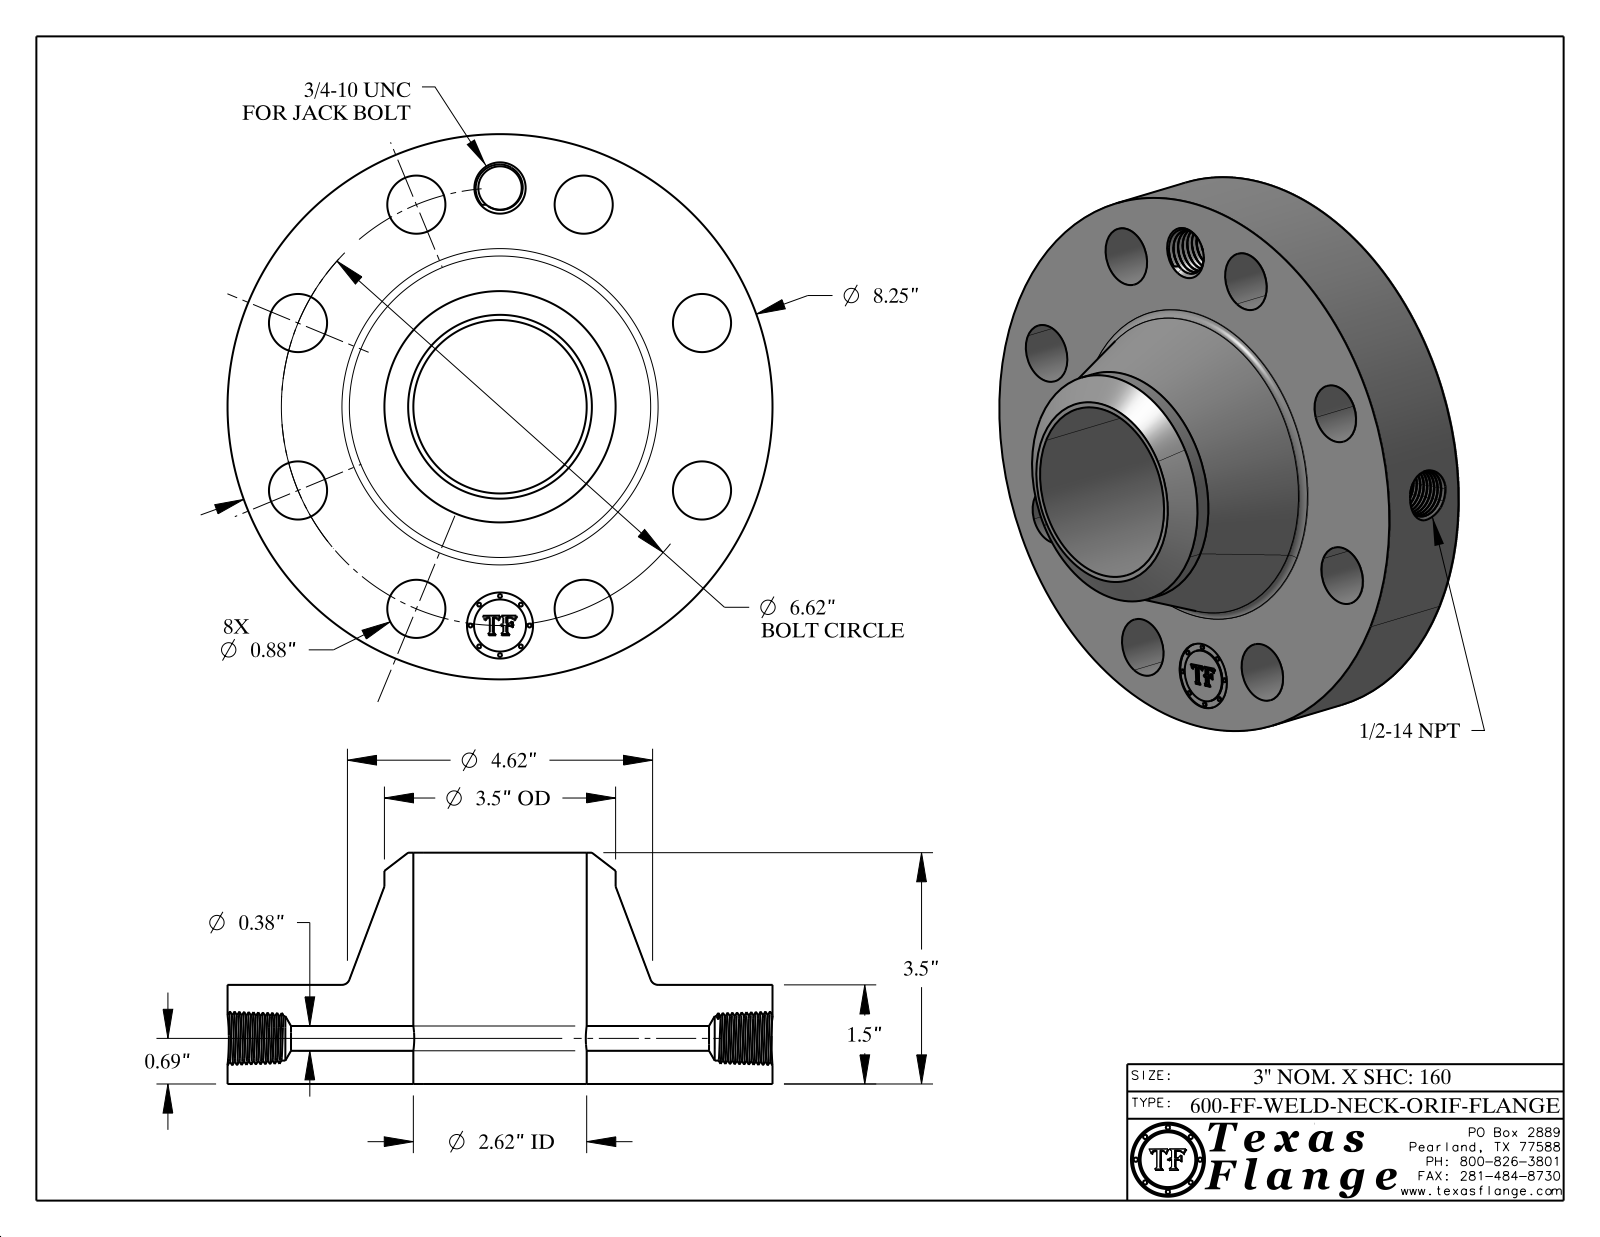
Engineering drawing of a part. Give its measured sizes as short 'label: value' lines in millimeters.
name: 600-FF-WELD-NECK
written by: CATIA V5 STEP AP214 (AUTOMOTIVE_DESIGN)
unit: mm
bodies: 1 solid, 766 faces (368 planar, 90 cylindrical, 308 other)
size: 209.6 × 209.6 × 88.9
volume: 1 246 000 mm³; area: 141 000 mm²
holes: 8× ⌀22.4, 1× ⌀9.5, 1× ⌀16.7, 1× ⌀17.1, 1× ⌀25.4, 1× ⌀66.6
bosses: 8× ⌀1.5, 1× ⌀209.6, 1× ⌀88.9, 1× ⌀20
face distances: 38.1, 88.9, 50.8, 0.4, 37.7, 51.2, 7.6, 7.4, 1.4, 6.3
hole spacings: 84.1, 118.9, 155.3, 168.1, 32.8, 64.3, 64.3, 93.4
